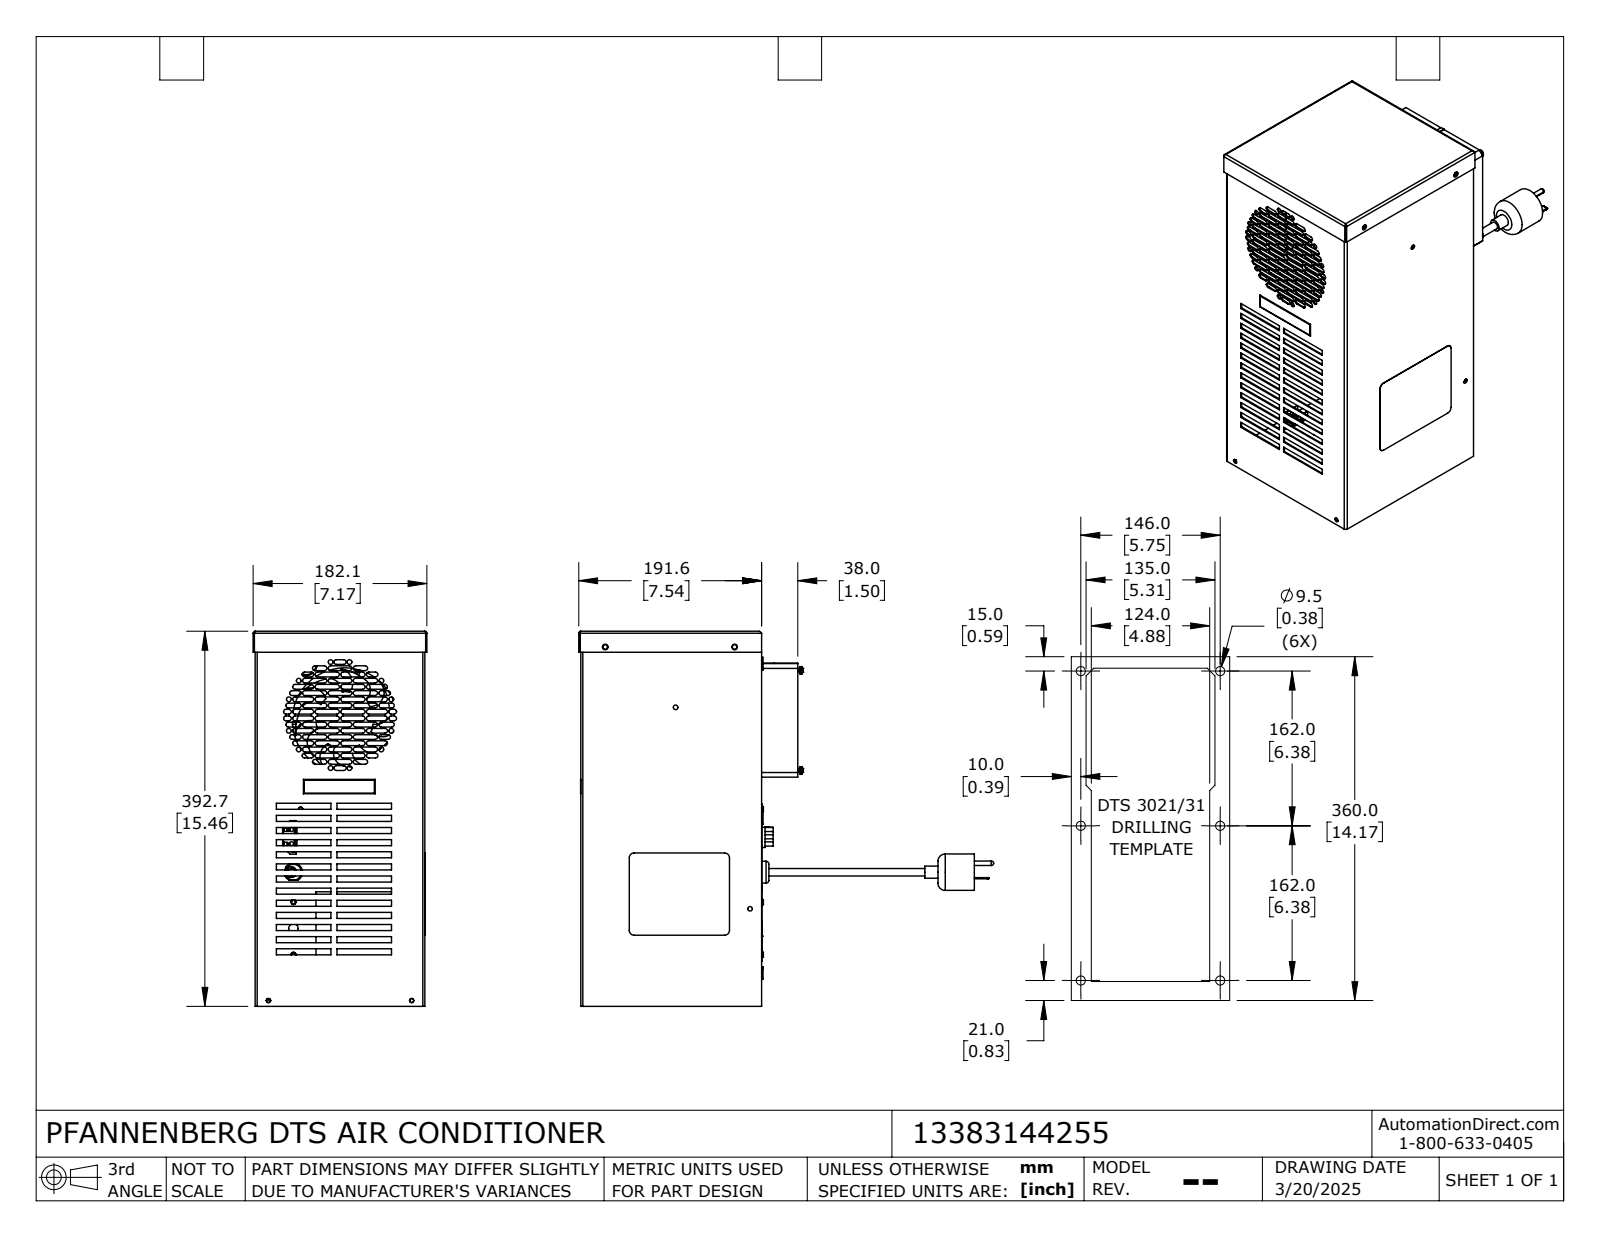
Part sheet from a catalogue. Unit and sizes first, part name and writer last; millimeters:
Units: millimetres
Overall size (bounding box): 434.7 × 392.7 × 182.1
Round holes (diameter × count): ⌀5 ×17, ⌀4.2 ×9, ⌀4.5 ×9, ⌀7.2 ×6, ⌀4.8 ×5, ⌀4.9 ×5, ⌀2.3 ×3, ⌀3.6 ×3, ⌀4 ×3, ⌀4.3 ×3, ⌀1.7 ×2, ⌀3.2 ×2
Round bosses / shafts (diameter × count): ⌀13 ×6, ⌀8 ×4, ⌀6.9 ×3, ⌀4 ×3, ⌀12.7 ×2, ⌀60 ×1, ⌀38.1 ×1, ⌀22.9 ×1
Partial cylindrical surfaces — rounded edges, fillets, slot ends (radius × count): R2.5 ×140, R0.5 ×12, R0.9 ×8, R2.1 ×8, R1 ×7, R13.9 ×7, R15.2 ×7, R56.5 ×7
Main face-to-face distances: 1.2, 176.6, 188.2, 2.1, 174.5, 177.8, 175.4, 187, 189.4, 175.7
Hole centre spacings: 7.4, 74.1, 104.8, 218.1, 56.6, 146, 162, 7.5
Volume: 880 100 mm³ · Surface area: 925 200 mm²
Bodies: 27 solids, 2834 faces (1494 planar, 695 cylindrical, 645 other)
Part name (STEP PRODUCT): 13383144255_Default
STEP written by: SolidWorks 2024 (CONFIG_CONTROL_DESIGN)
